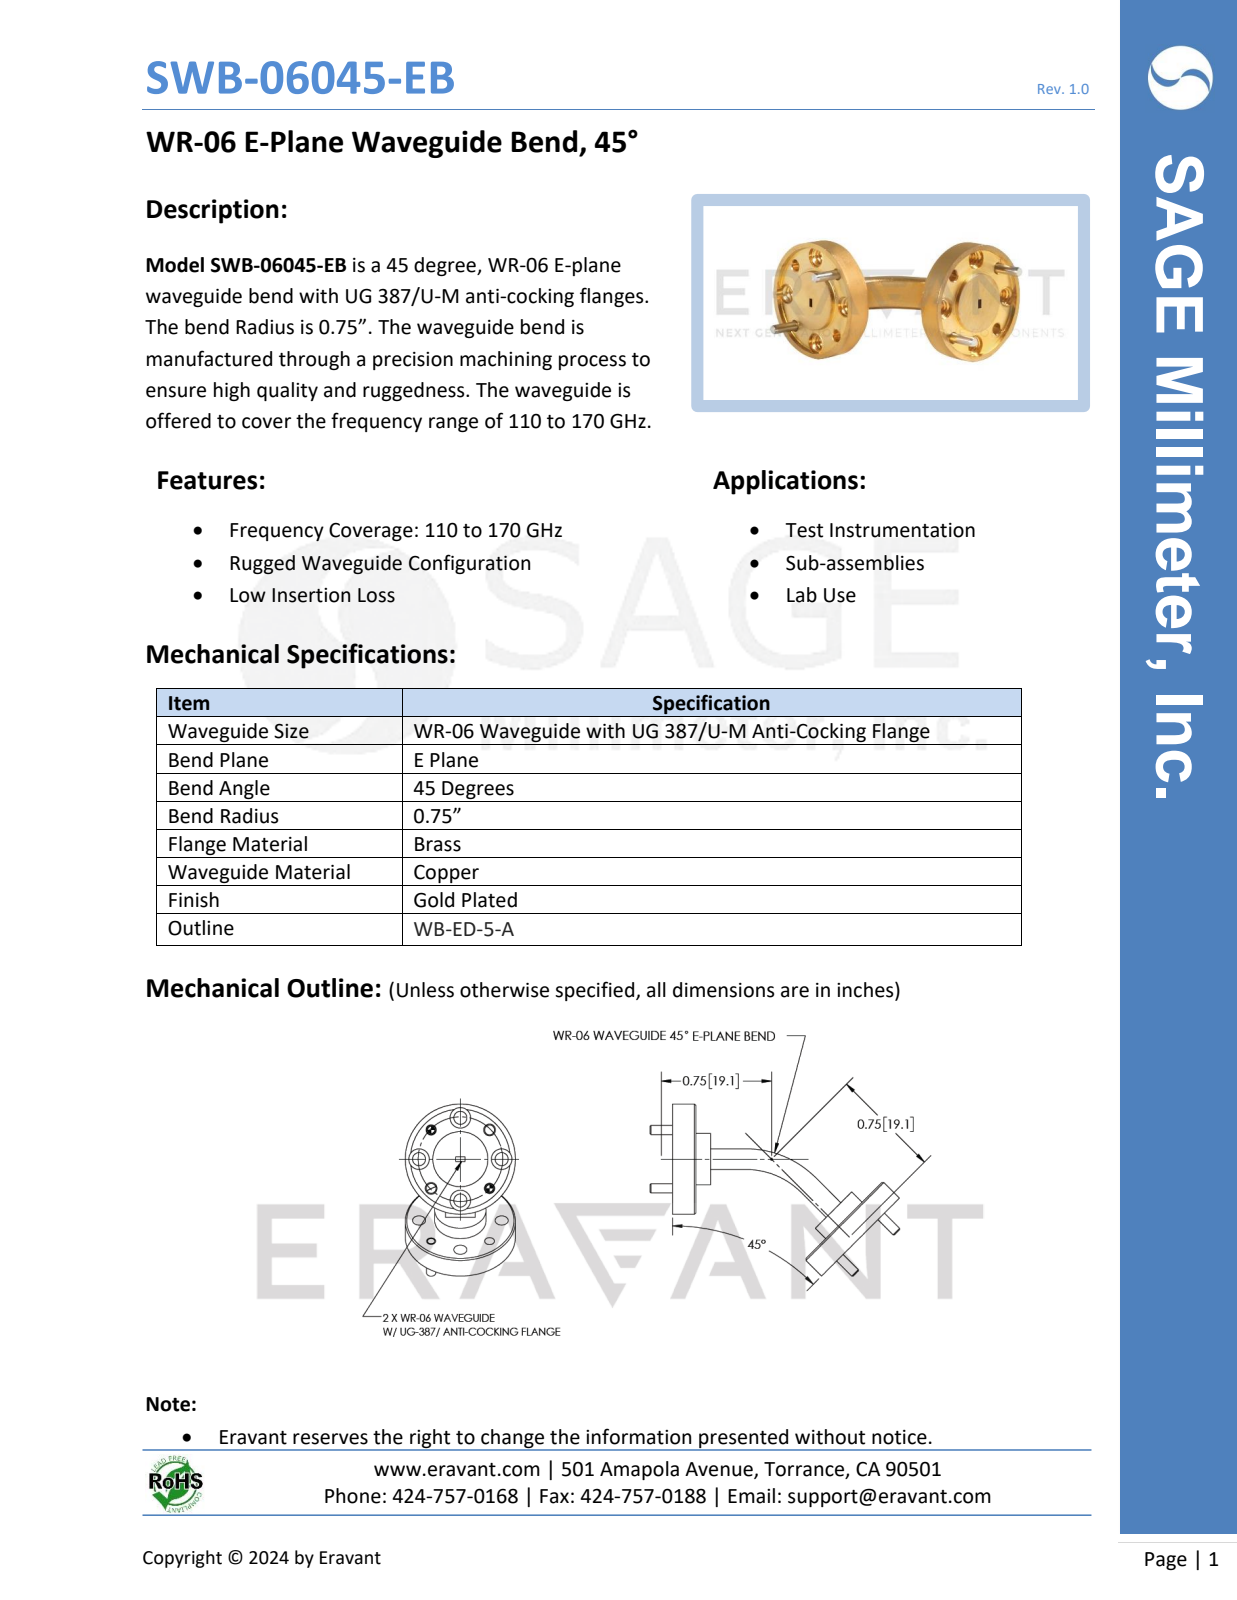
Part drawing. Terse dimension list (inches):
name: WB-ED-5-A, Rev 1.0, CTRLD
written by: SolidWorks 2021 (AUTOMOTIVE_DESIGN)
unit: in
bodies: 5 solids, 156 faces (42 planar, 78 cylindrical, 36 other)
size: 1.699 × 1.171 × 0.75
volume: 0.167 in³; area: 4.154 in²
holes: 8× ⌀0.089, 8× ⌀0.14, 4× ⌀0.061, 4× ⌀0.067, 2× ⌀0.68
bosses: 4× ⌀0.063, 2× ⌀0.75, 2× ⌀0.375, 2× ⌀0.35
rounds: 1× R0.529, 1× R0.671
face distances: 0.02, 0.1, 0.16, 0.16, 0.14, 0.14, 0.202, 0.141, 0.2, 0.24
hole spacings: 0.281, 0.398, 0.215, 0.519, 0.562, 0.215, 0.52
